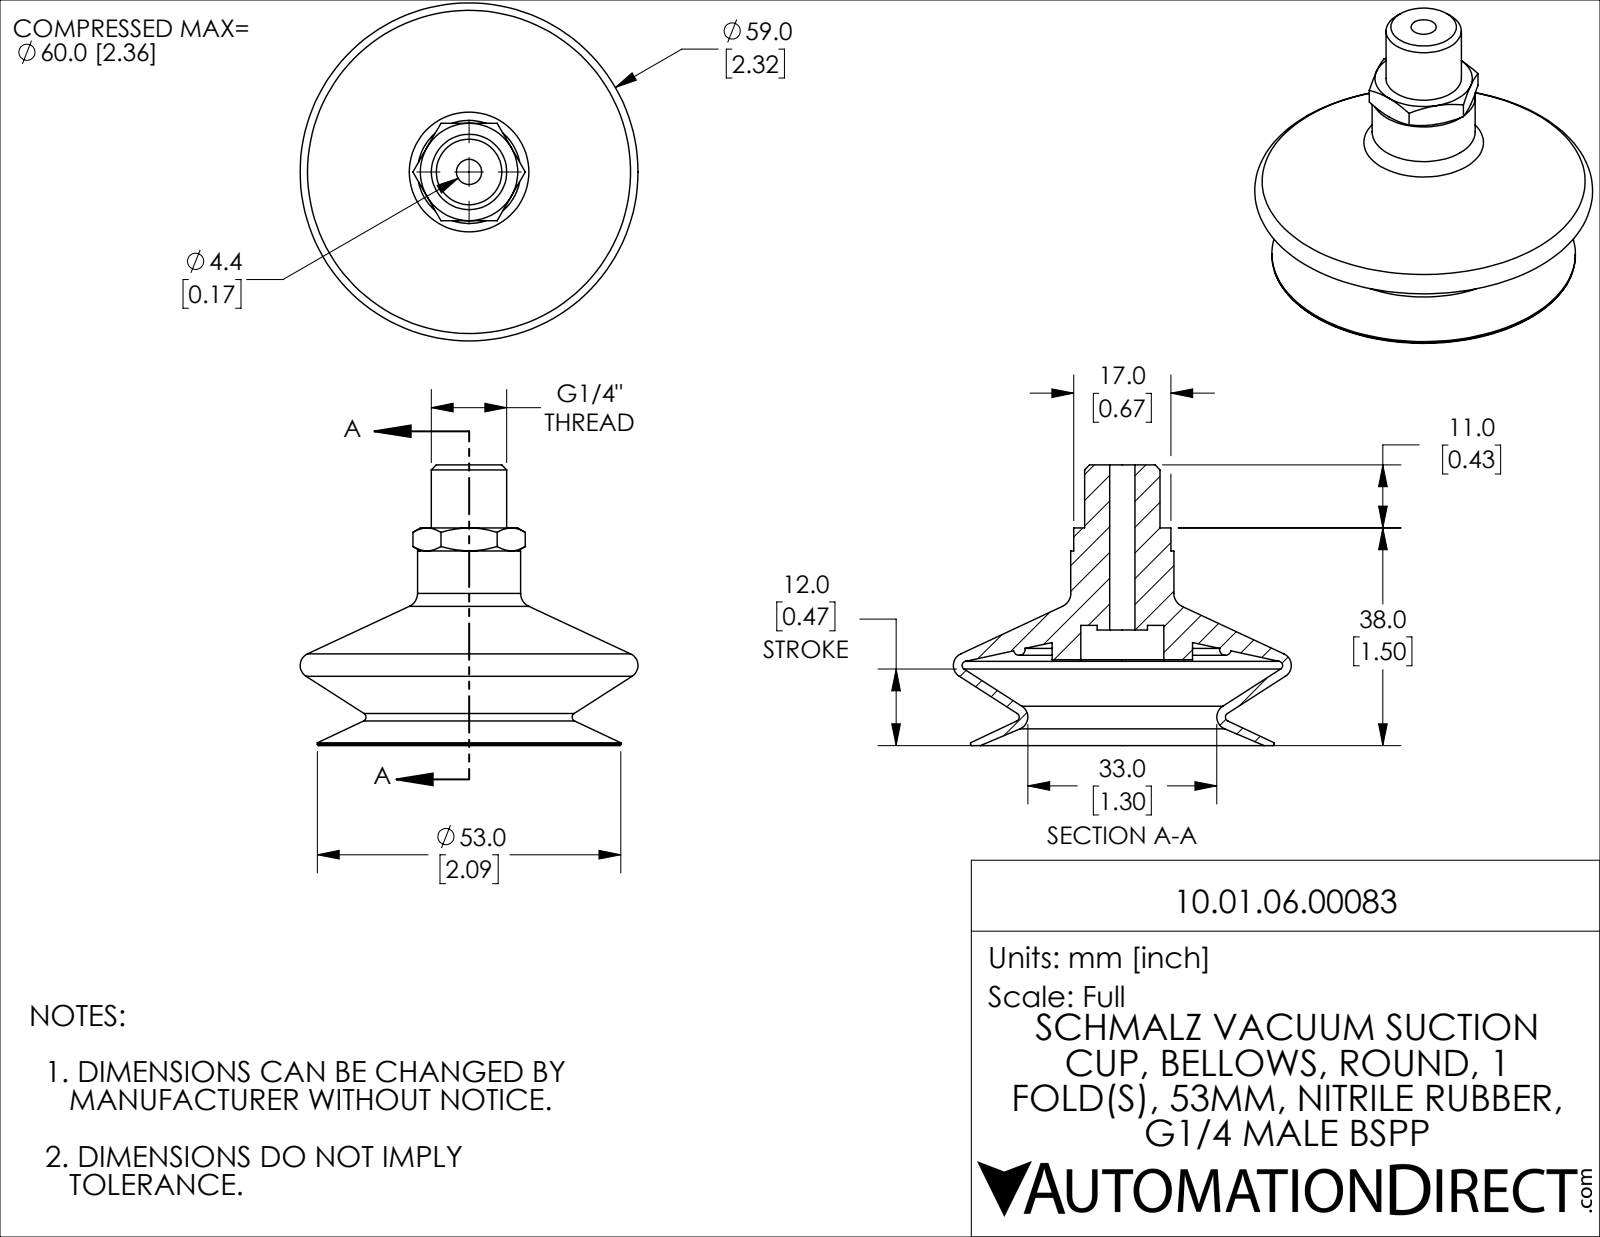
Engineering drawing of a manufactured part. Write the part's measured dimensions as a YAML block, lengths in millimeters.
part_name: "10.01.06.00083"
step_written_by: "SolidWorks 2021 (CONFIG_CONTROL_DESIGN)"
units: millimeters
bodies: {solids: 1, faces: 79, planar: 13, cylindrical: 12, other: 54}
overall_size: [59, 59, 49]
volume: 20128
surface_area: 15306
round_holes:
  - {diameter: 4.4, count: 1}
  - {diameter: 14.5, count: 1}
round_bosses_or_shafts:
  - {diameter: 53, count: 1}
  - {diameter: 24.5, count: 1}
  - {diameter: 13.16, count: 1}
  - {diameter: 8.8, count: 1}
face_to_face_distances: [15, 17, 34, 21, 6, 38, 23, 49, 28, 11]
